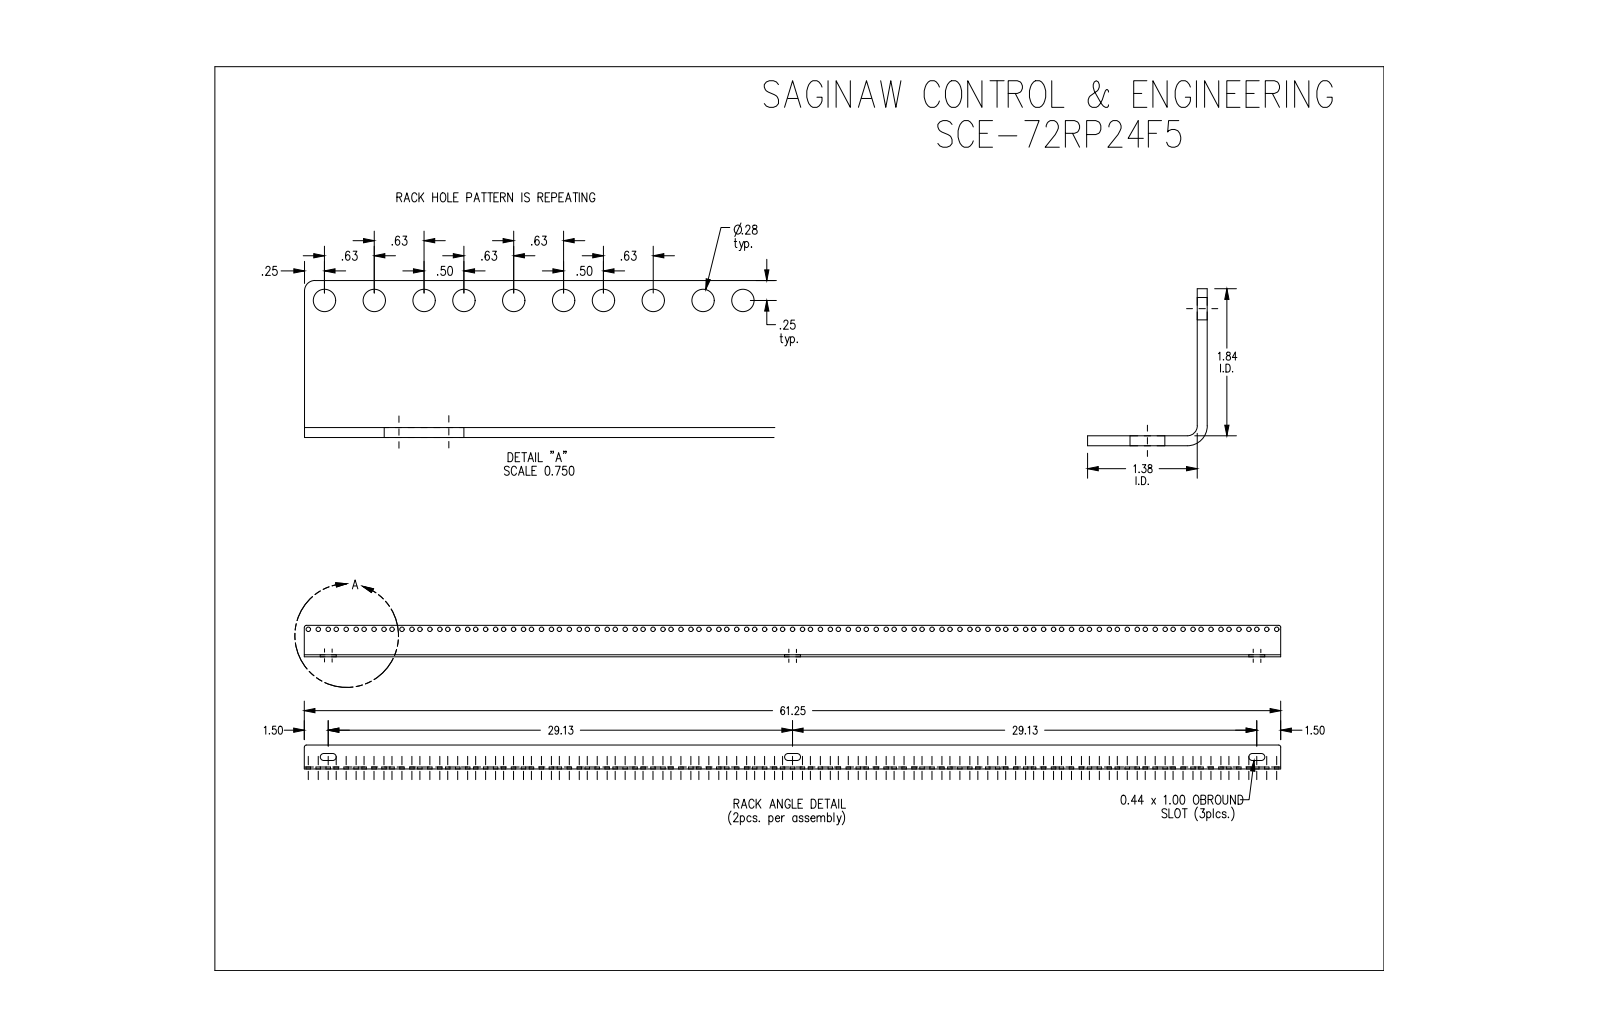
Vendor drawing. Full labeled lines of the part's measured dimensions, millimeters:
Part name (STEP PRODUCT): SCE-72RP24F5
STEP written by: SolidWorks 2019 (CONFIG_CONTROL_DESIGN)
Units: millimetres
Bodies: 2 solids, 262 faces (28 planar, 234 cylindrical, 0 other)
Overall size (bounding box): 1555.8 × 552.5 × 38.1
Volume: 787 200 mm³ · Surface area: 532 900 mm²
Round holes (diameter × count): ⌀7.1 ×210
Partial cylindrical surfaces — rounded edges, fillets, slot ends (radius × count): R5.6 ×6, R3.2 ×4, R3.3 ×4, R6.4 ×2
Main face-to-face distances: 3.2, 546.1, 549.3, 3.2, 549.3, 552.5, 46.8, 499.3, 38.1, 34.9
Hole centre spacings: 44.5, 88.9, 133.4, 177.8, 222.3, 15.9, 15.9, 31.8
